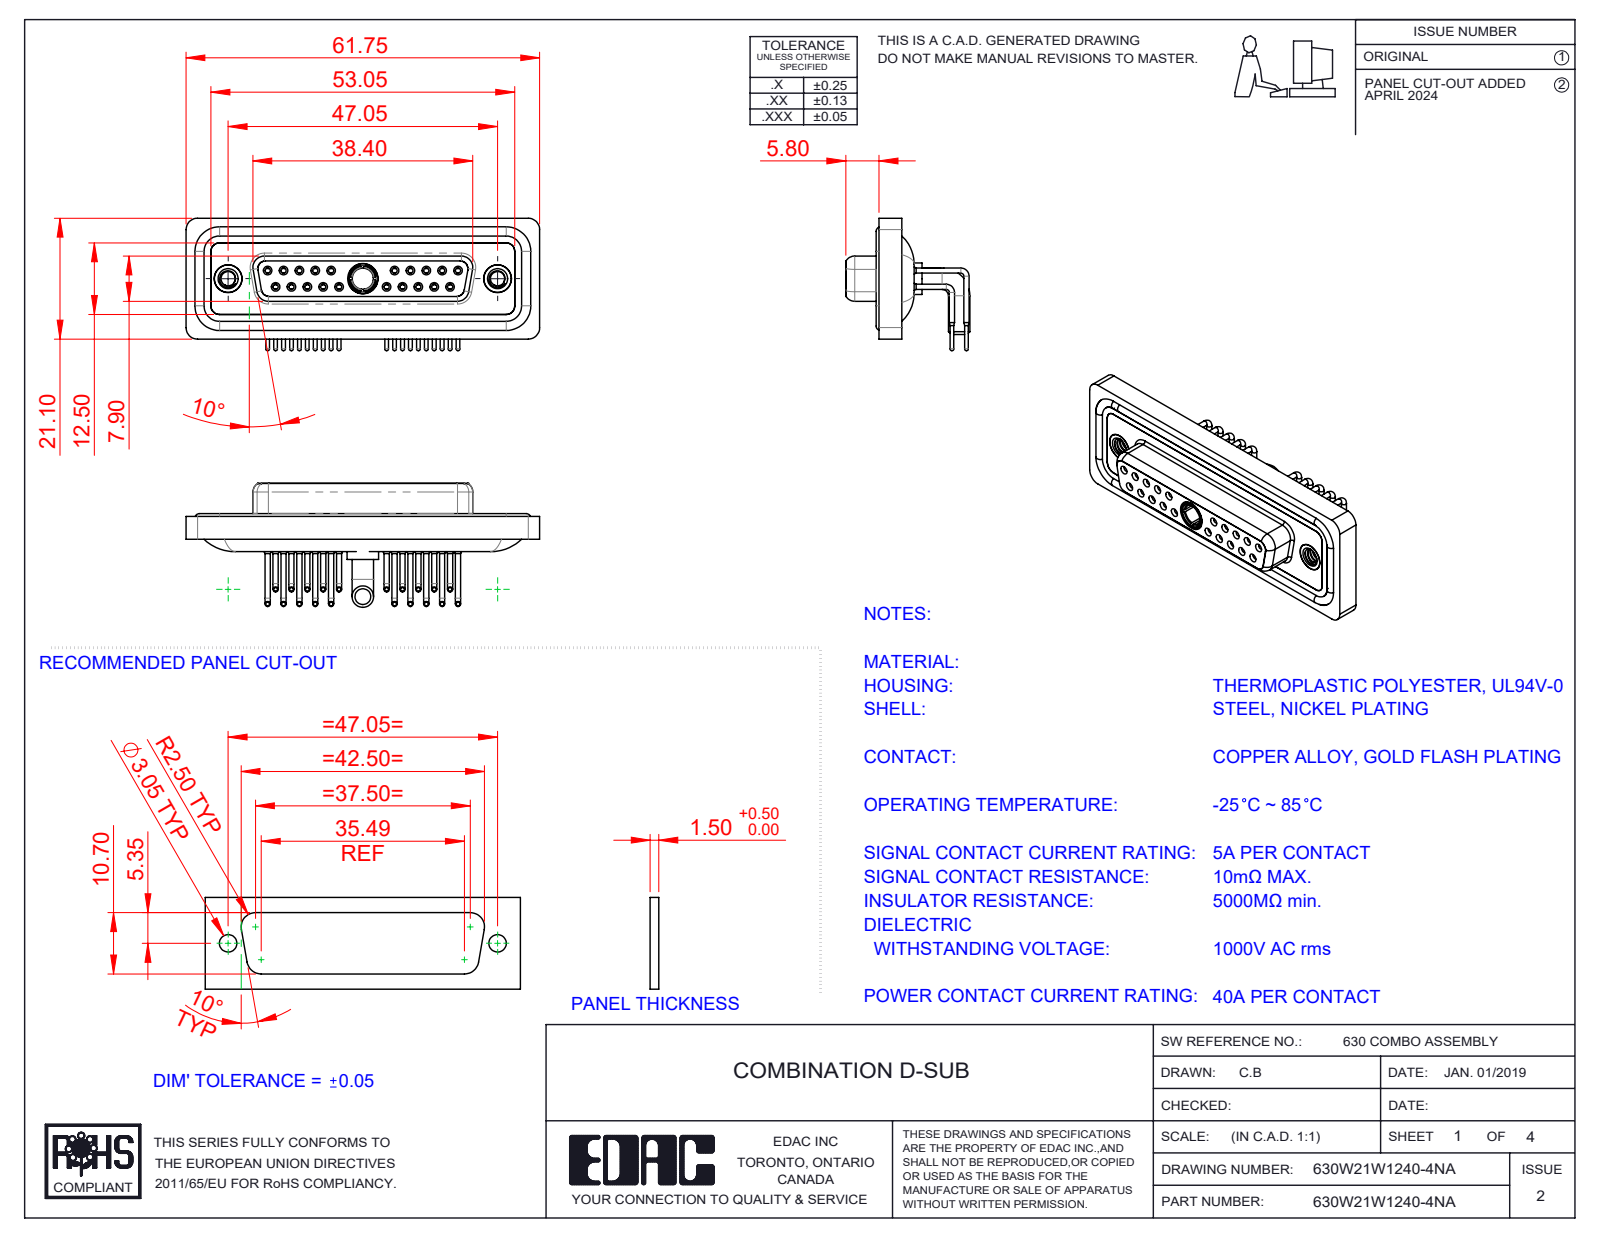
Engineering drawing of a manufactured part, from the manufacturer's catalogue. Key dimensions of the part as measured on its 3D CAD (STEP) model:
Part name (STEP PRODUCT): 630Combo Shell Rear_25 Contacts; 630Combo Contact Row 1_50 Contacts; 630Combo Waterproof Housing_25 Contacts; 630Combo Shell Front_25 Contacts (+5 more)
STEP written by: SolidWorks 2023 (CONFIG_CONTROL_DESIGN)
Units: millimetres
Bodies: 29 solids, 1518 faces (434 planar, 671 cylindrical, 413 other)
Overall size (bounding box): 61.75 × 23.12 × 21.68
Volume: 8 571 mm³ · Surface area: 14 827 mm²
Round holes (diameter × count): ⌀0.9 ×20, ⌀1.1 ×20, ⌀1.5 ×20, ⌀2 ×20, ⌀1.6 ×10, ⌀1.7 ×10, ⌀4.85 ×3, ⌀2.5 ×2, ⌀4 ×2, ⌀4.05 ×2, ⌀5 ×2, ⌀3.7 ×1
Round bosses / shafts (diameter × count): ⌀0.9 ×20, ⌀0.65 ×20, ⌀1.6 ×14, ⌀4.95 ×2, ⌀4.8 ×2, ⌀3.75 ×2, ⌀5.5 ×1, ⌀5.2 ×1
Partial cylindrical surfaces — rounded edges, fillets, slot ends (radius × count): R1.5 ×18, R2 ×18, R1.35 ×8, R1.6 ×8, R0.25 ×4, R0.5 ×4, R0.6 ×4, R0.65 ×4
Main face-to-face distances: 0.4, 1.8, 4.1, 1.6, 1.1, 2.5, 3.1, 1.5, 9.8, 0.45
Hole centre spacings: 3.16, 2.77, 5.54, 8.31, 5.04, 19.39, 20.97, 22.16
